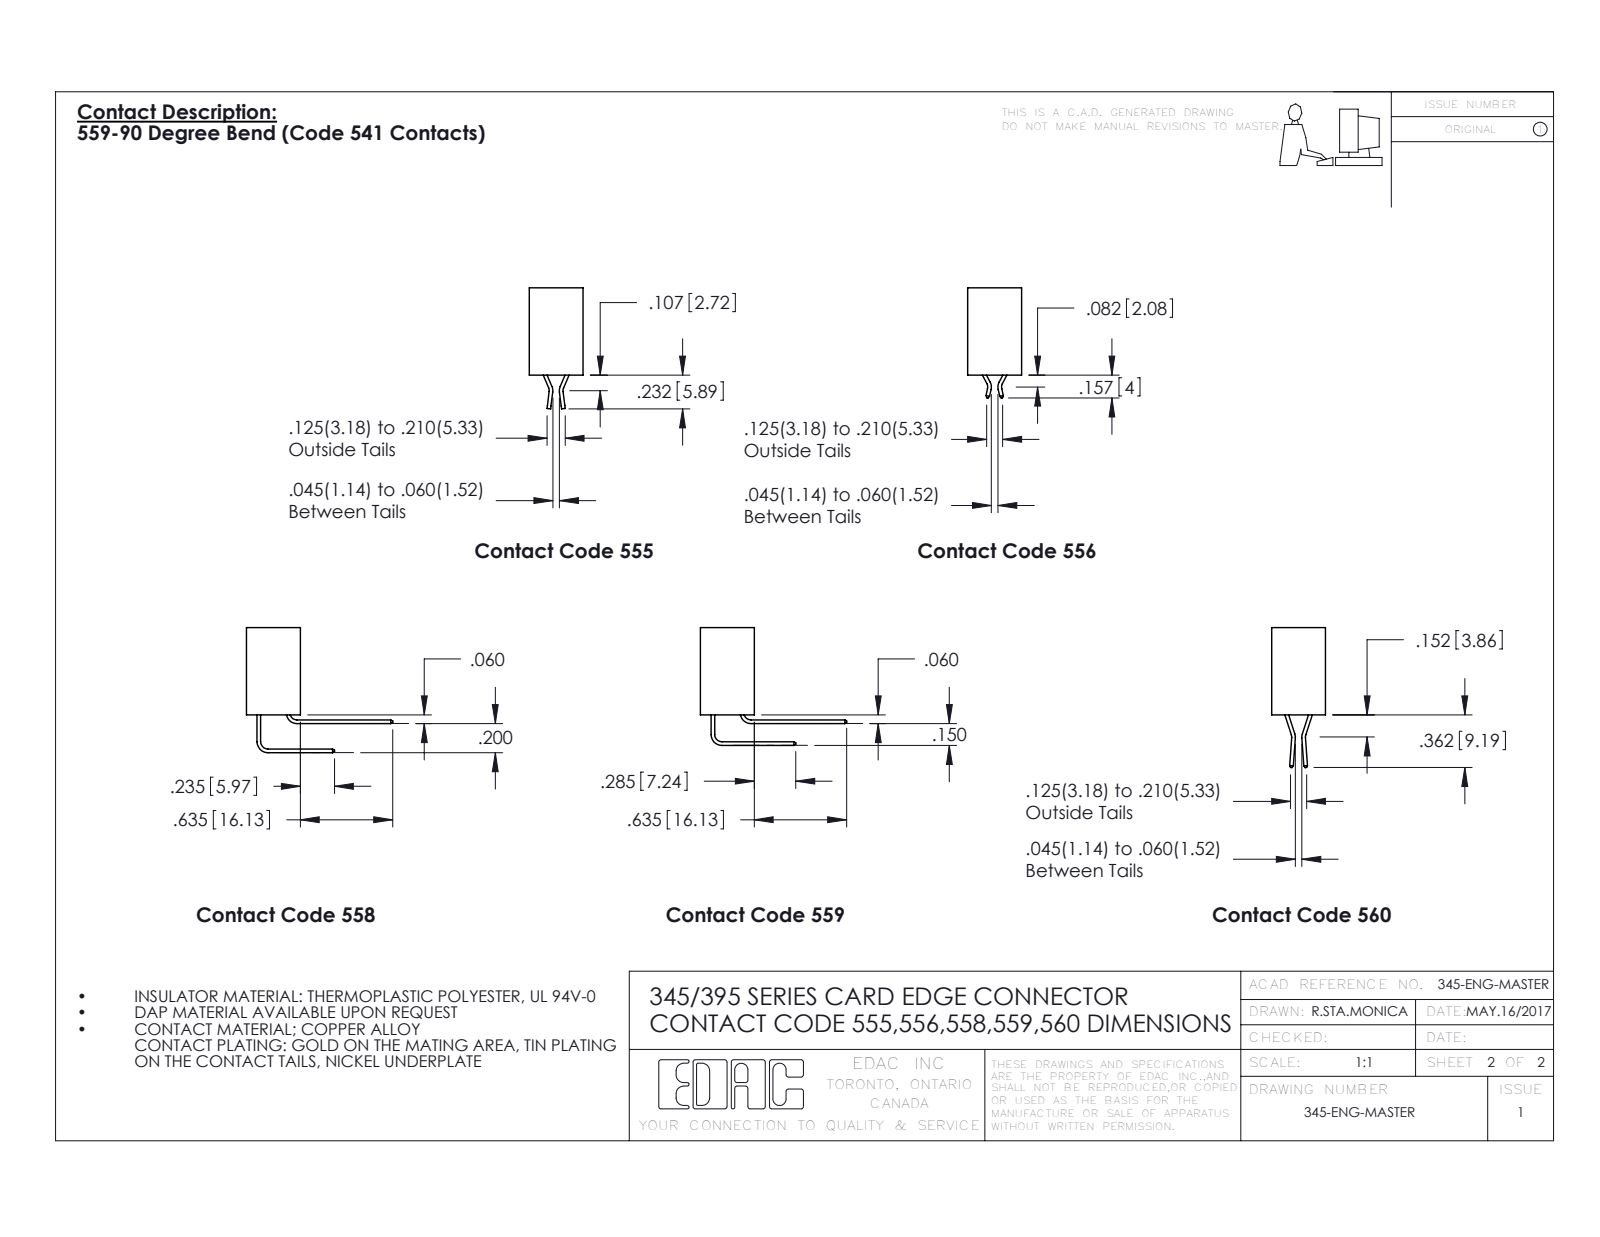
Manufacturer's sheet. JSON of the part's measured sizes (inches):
{"part_name": "345-292-001_345-293-120; 395-060-520-101; 345 Part_No Mounting Lugs", "step_written_by": "SolidWorks 2016 (CONFIG_CONTROL_DESIGN)", "units": "inches", "bodies": {"solids": 61, "faces": 3838, "planar": 2596, "cylindrical": 1242, "other": 0}, "overall_size": [6.26, 0.775, 0.37], "volume_in3": 0.956, "surface_area_in2": 32.06, "round_holes": [[0.064, 1]], "partial_cylinders_radius": [[0.01, 122], [0.006, 120], [0.01, 22], [0.007, 6], [0.031, 6], [0.026, 3], [0.031, 2], [0.04, 2]], "face_to_face_distances": [0.298, 0.072, 0.37, 0.2, 0.098, 0.272, 0.025, 0.225, 0.072, 0.149]}
